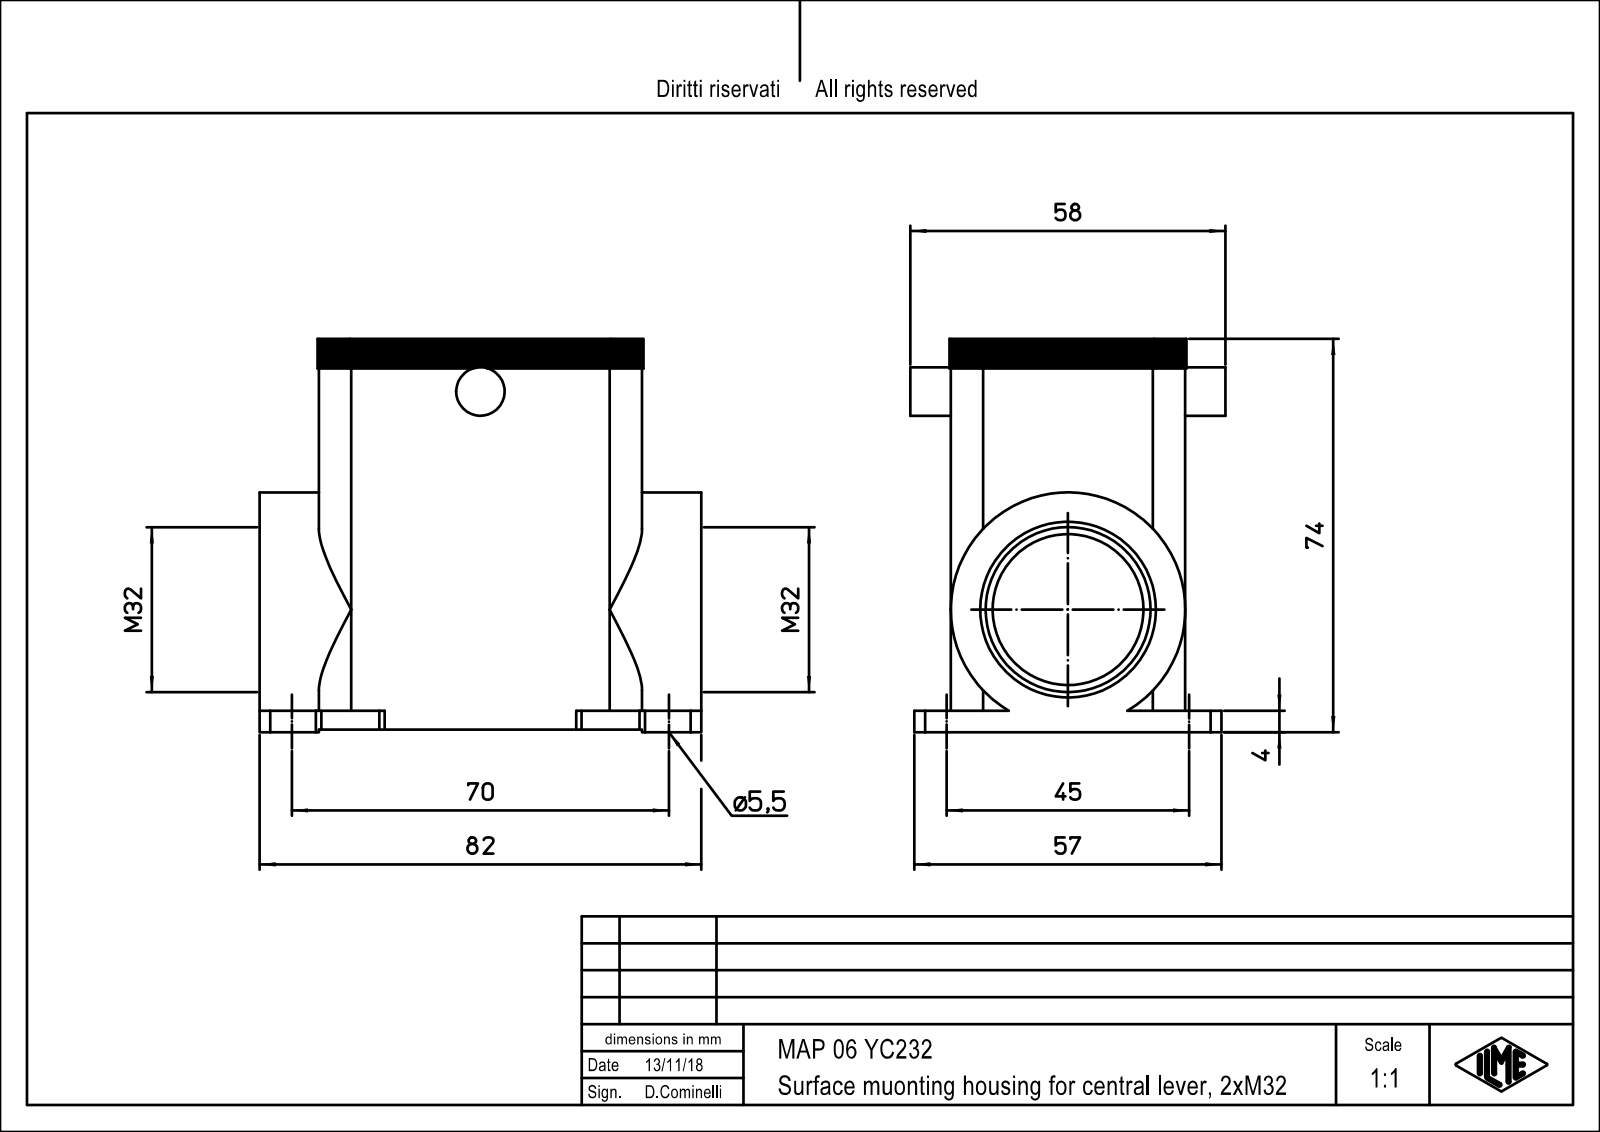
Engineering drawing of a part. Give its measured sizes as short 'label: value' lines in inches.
name: MAP_06_YC232
written by: PTC Creo Elements/Direct Modeling 19.0E 27-Jun-2016 (C) Parametric Technology GmbH (AUTOMOTIVE_DESIGN)
unit: in
bodies: 1 solid, 141 faces (64 planar, 66 cylindrical, 11 other)
size: 3.228 × 2.874 × 2.303
volume: 5.118 in³; area: 60.32 in²
holes: 4× ⌀0.097, 4× ⌀0.217, 1× ⌀1.102, 1× ⌀1.205
bosses: 1× ⌀1.713, 1× ⌀0.354
rounds: 16× R0.079, 8× R0.236, 4× R0.059, 4× R0.118
face distances: 0.118, 1.594, 1.713, 1.476, 0.138, 0.157, 2.382, 0.433, 0.413, 1.949
hole spacings: 0.622, 1.507, 2.272, 2.654, 1.063, 1.732, 1.772, 2.032
